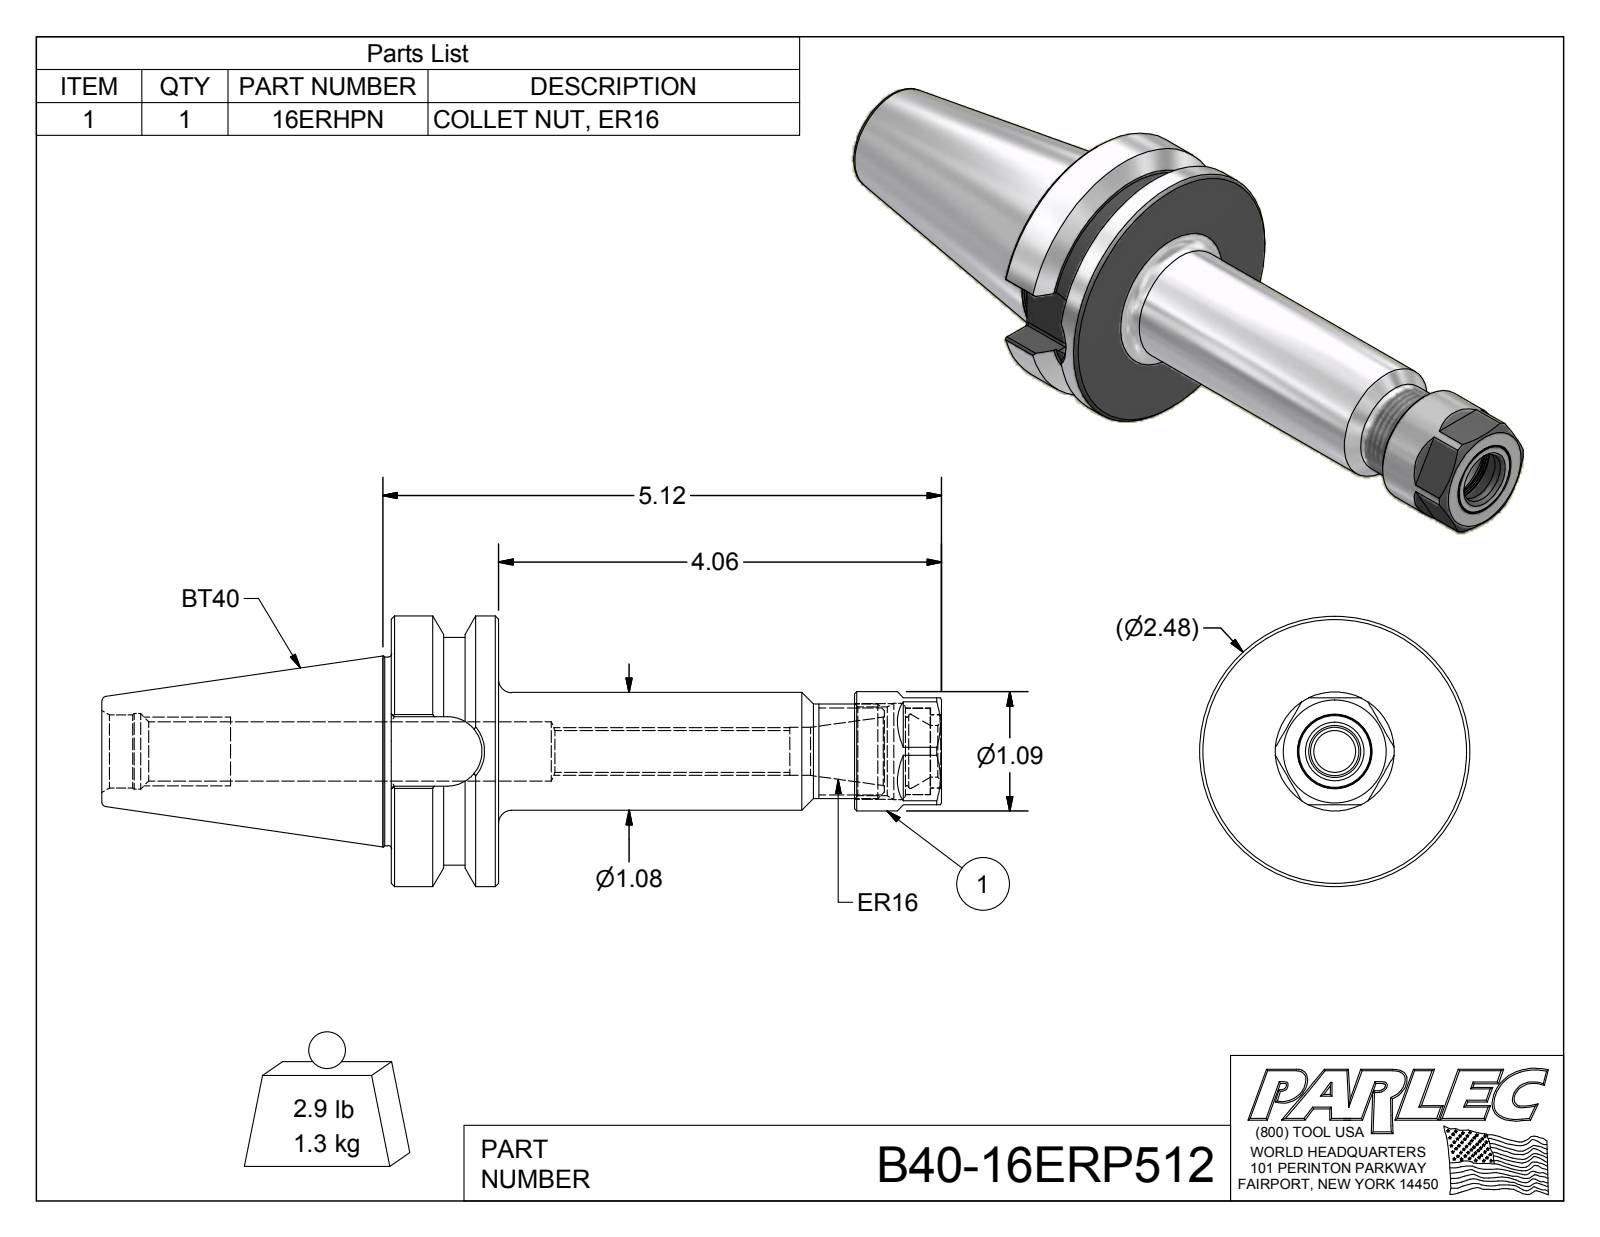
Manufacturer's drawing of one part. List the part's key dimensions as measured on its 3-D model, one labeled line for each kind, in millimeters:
Part name (STEP PRODUCT): B40-16ERP512; B40-16ER5-1; 16ERHPN
STEP written by: Autodesk Inventor 2012 (AUTOMOTIVE_DESIGN)
Units: millimetres
Bodies: 3 solids, 114 faces (44 planar, 33 cylindrical, 37 other)
Overall size (bounding box): 195.5 × 63 × 63
Volume: 165 700 mm³ · Surface area: 37 490 mm²
Round holes (diameter × count): ⌀9.7 ×1, ⌀11.2 ×1, ⌀12 ×1, ⌀13.8 ×1, ⌀16 ×1, ⌀17 ×1, ⌀17.1 ×1, ⌀17.3 ×1, ⌀17.6 ×1, ⌀20.2 ×1, ⌀20.7 ×1, ⌀22.4 ×1
Round bosses / shafts (diameter × count): ⌀63 ×1, ⌀53 ×1, ⌀43.9 ×1, ⌀27.7 ×1, ⌀27.4 ×1, ⌀22 ×1, ⌀20.1 ×1, ⌀17 ×1
Partial cylindrical surfaces — rounded edges, fillets, slot ends (radius × count): R0.5 ×8, R8.1 ×1
Main face-to-face distances: 25, 24.9, 45.2, 128.1, 103.1, 4.4, 20.5, 107.8, 82.9, 20.2
